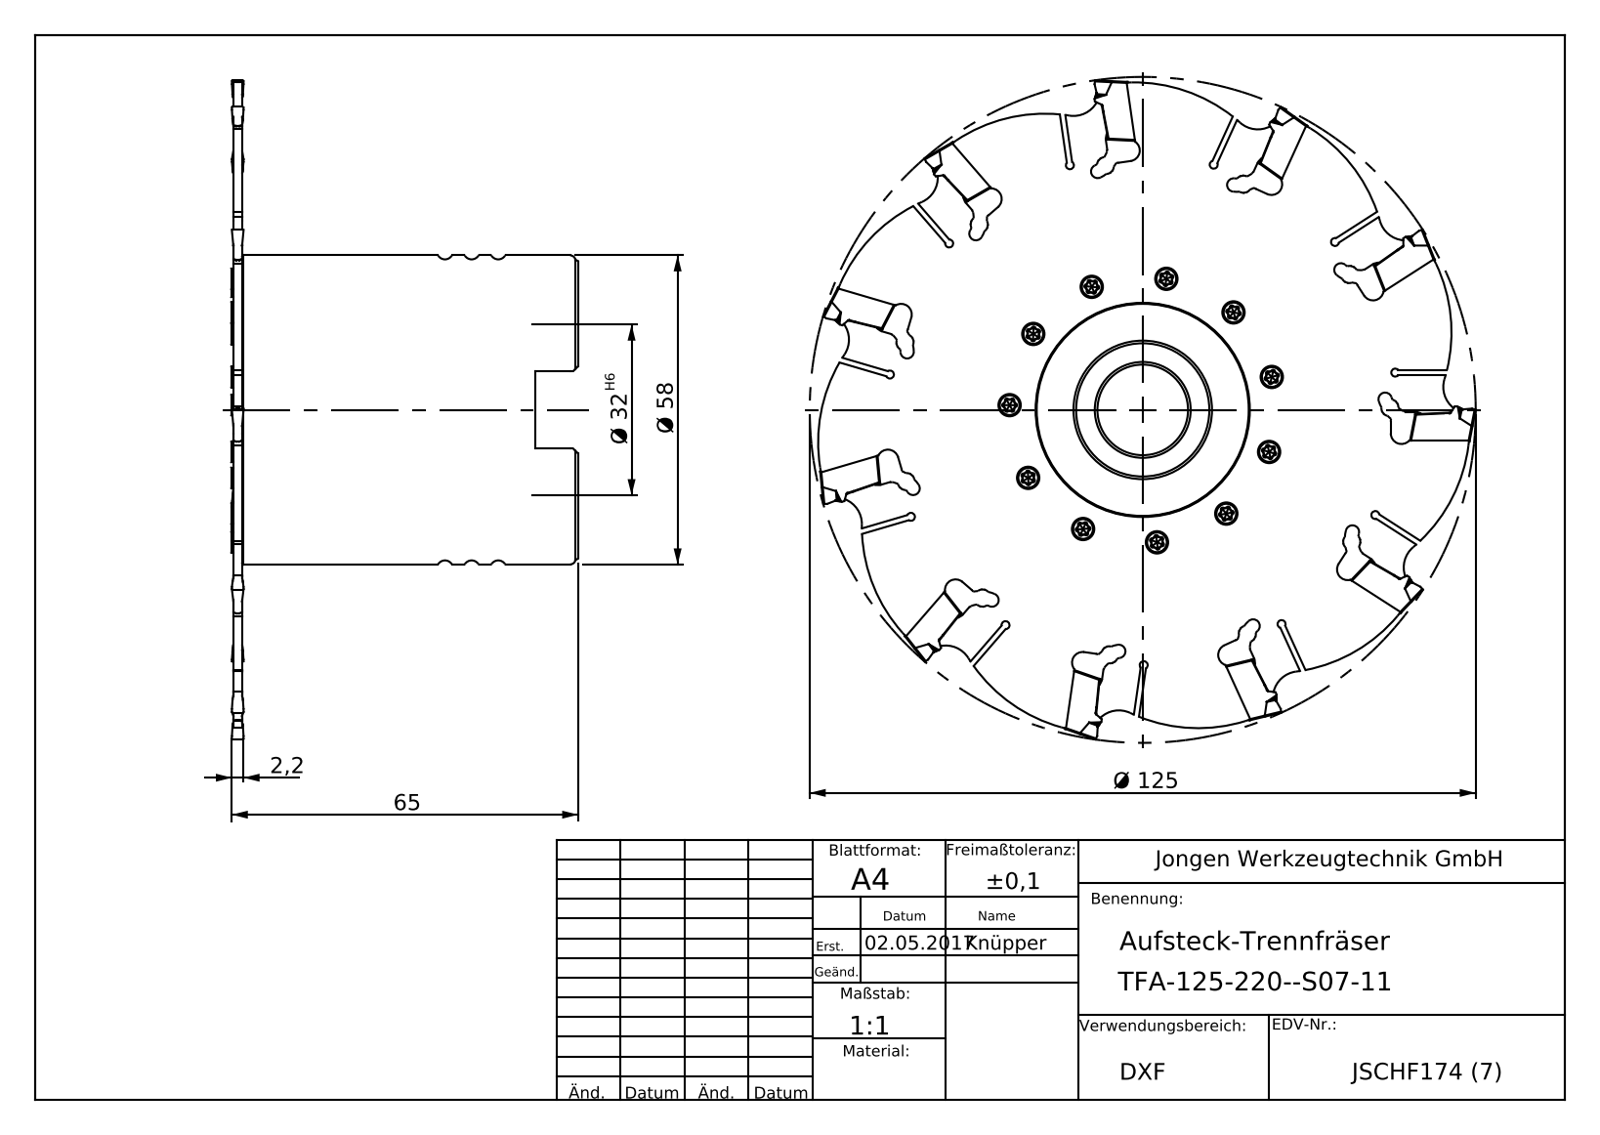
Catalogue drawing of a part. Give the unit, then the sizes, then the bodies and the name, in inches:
Units: inches
Overall size (bounding box): 4.921 × 4.921 × 2.559
Round holes (diameter × count): ⌀0.098 ×11, ⌀0.126 ×11, ⌀0.165 ×11, ⌀0.669 ×1, ⌀0.984 ×1, ⌀1.26 ×1, ⌀1.266 ×1, ⌀1.272 ×1, ⌀1.575 ×1
Round bosses / shafts (diameter × count): ⌀4.921 ×1, ⌀2.283 ×1
Main face-to-face distances: 0.076, 0.085, 0.067, 2.473, 2.482, 2.549, 2.558, 1.565, 0.669, 0.984
Hole centre spacings: 0.984, 1.948, 0.555, 1.791, 1.064, 1.488, 0.557, 1.062
Volume: 9.266 in³ · Surface area: 70.25 in²
Bodies: 2 solids, 216 faces (20 planar, 90 cylindrical, 106 other)
Part name (STEP PRODUCT): JSCHF174 pk_Kontrolle; TFA-125-220-S07-11; JSCHF174_1 pk
STEP written by: SolidWorks 2018 (AUTOMOTIVE_DESIGN)
